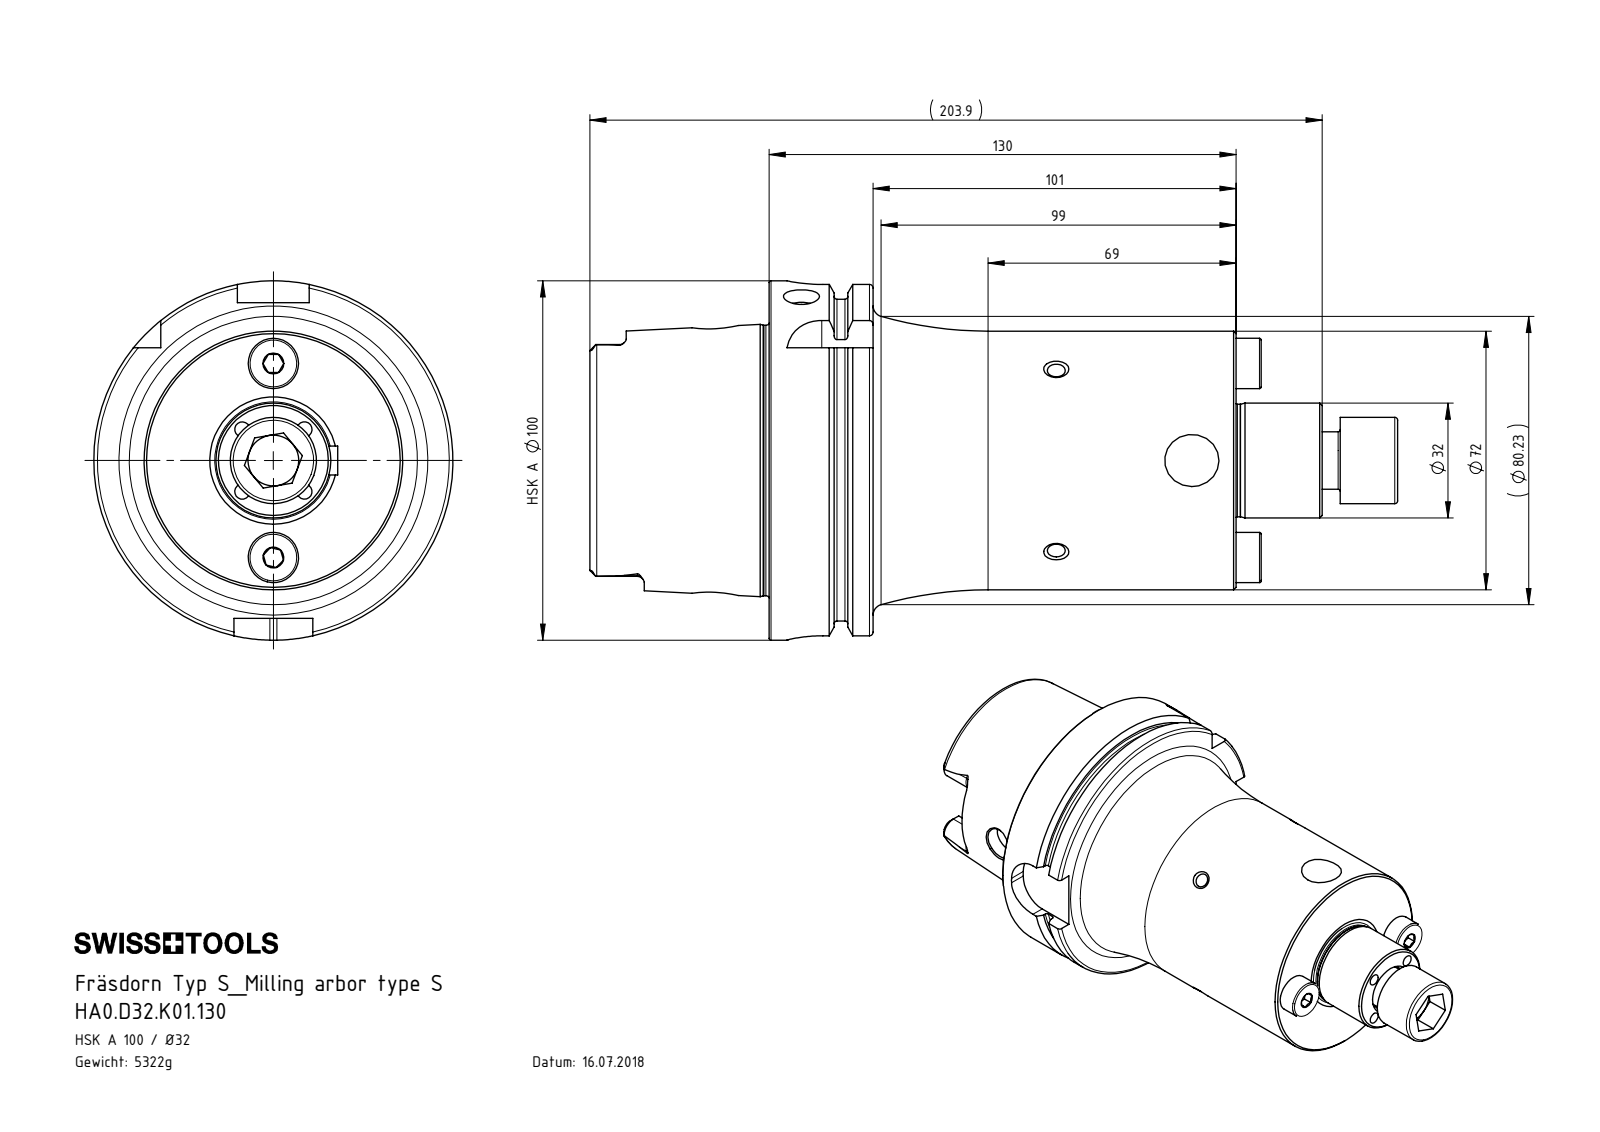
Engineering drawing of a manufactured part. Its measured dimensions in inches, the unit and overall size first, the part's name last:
Units: inches
Overall size (bounding box): 8.854 × 3.937 × 3.937
Round holes (diameter × count): ⌀0.165 ×6, ⌀0.197 ×6, ⌀0.472 ×4, ⌀0.394 ×3, ⌀0.551 ×1, ⌀0.669 ×1, ⌀0.886 ×1, ⌀1.024 ×1, ⌀2.087 ×1, ⌀2.48 ×1
Round bosses / shafts (diameter × count): ⌀0.551 ×2, ⌀0.236 ×2, ⌀0.181 ×2, ⌀3.937 ×1, ⌀3.62 ×1, ⌀2.963 ×1, ⌀2.835 ×1, ⌀1.26 ×1
Partial cylindrical surfaces — rounded edges, fillets, slot ends (radius × count): R0.075 ×6, R0.157 ×4, R0.192 ×4, R0.394 ×4
Main face-to-face distances: 5.118, 1.14, 3.978, 0.49, 0.65, 4.628, 1.965, 2.455, 3.104, 7.083
Hole centre spacings: 0.482, 0.682, 0.798, 1.445, 1.577, 0.964, 1.063, 2.126
Volume: 42.04 in³ · Surface area: 139.7 in²
Bodies: 5 solids, 371 faces (89 planar, 119 cylindrical, 163 other)
Part name (STEP PRODUCT): ISO 4762 - M16 x 35; HA0-D32.K01.130_B_Fertigbearbeitung; D32-ER2.001.022_B; HA0.D32.K01.130 (+1 more)
STEP written by: SolidWorks 2017 (AUTOMOTIVE_DESIGN)
